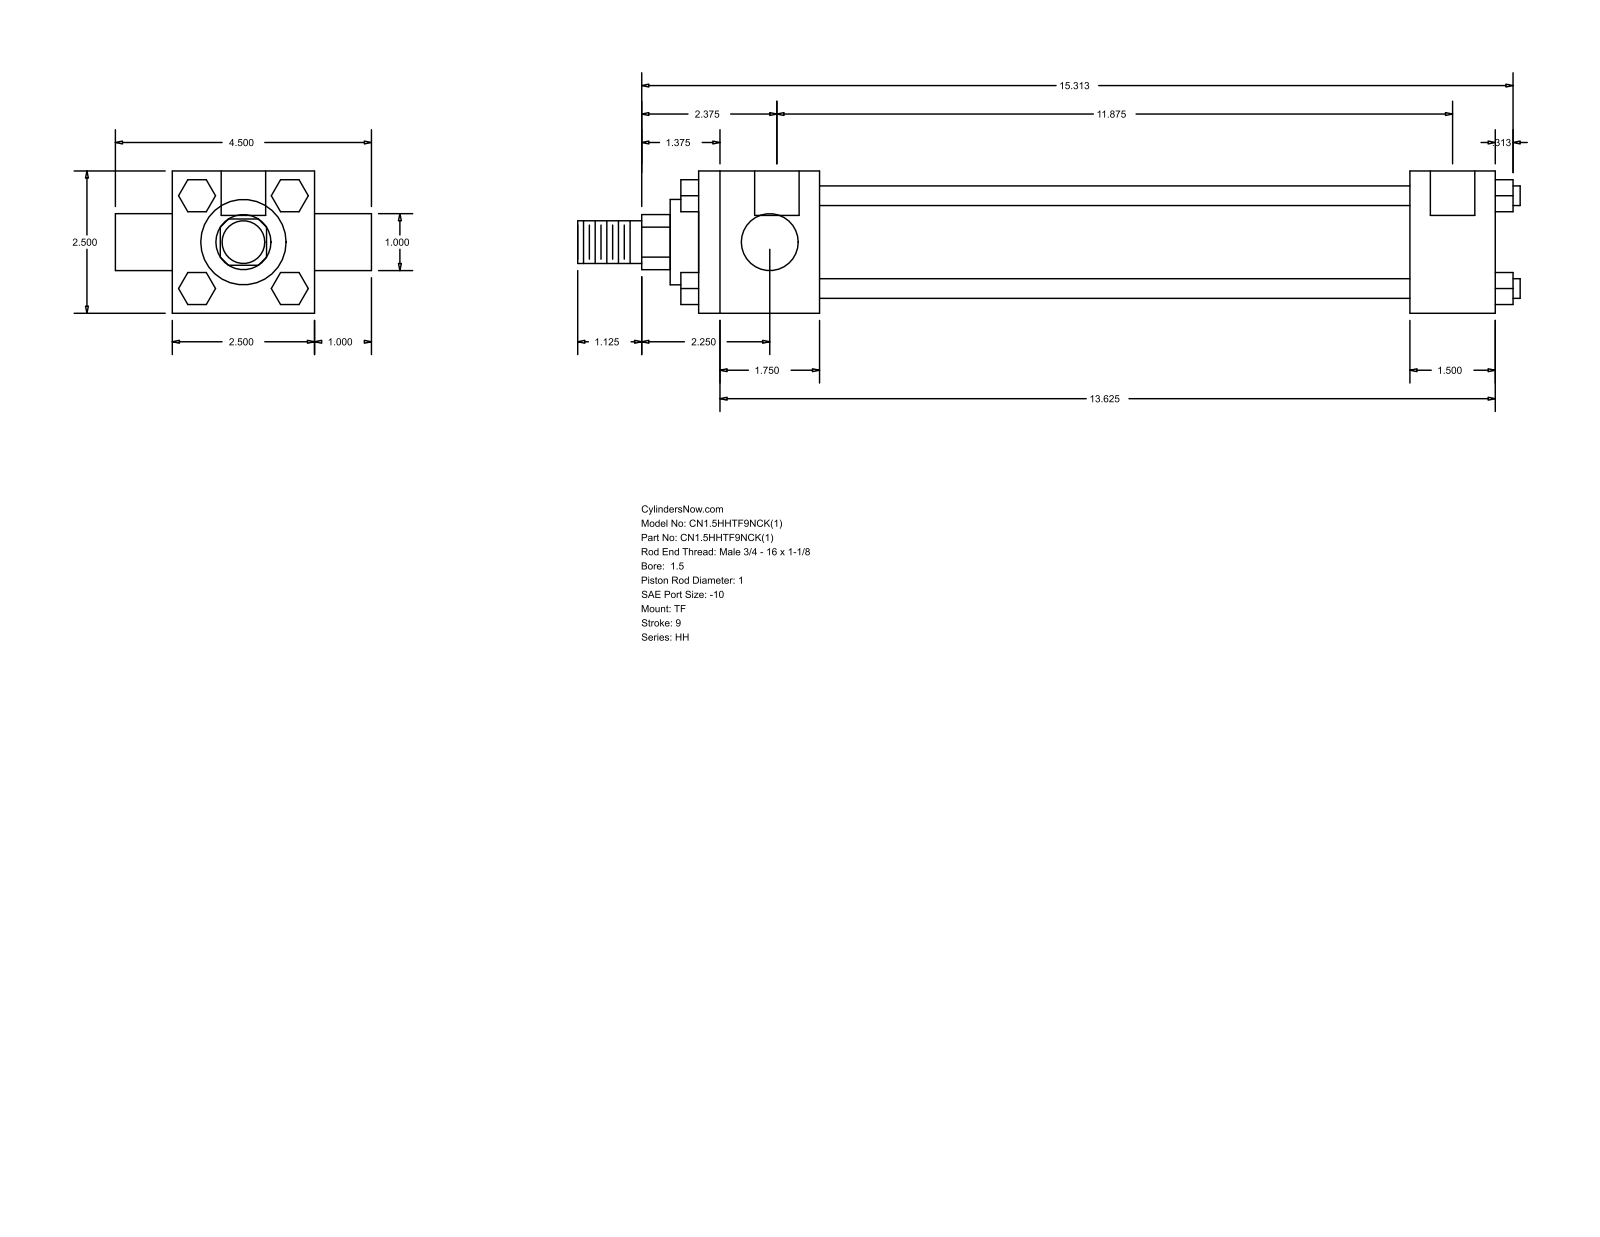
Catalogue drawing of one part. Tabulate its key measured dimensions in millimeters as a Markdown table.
| quantity | value |
| --- | --- |
| part name | HH_TF__0150_1 |
| STEP written by | GSSL Pune (CONFIG_CONTROL_DESIGN) |
| units | millimeters |
| bodies | 0 solids, 120 faces (92 planar, 28 cylindrical, 0 other) |
| overall size | 420.69 × 114.3 × 63.5 |
| round holes (diameter × count) | 5.56 × 3, 19.84 × 2 |
| round bosses / shafts (diameter × count) | 8.76 × 4, 25.4 × 2, 44.45 × 1, 38.1 × 1, 19.05 × 1 |
| partial cylindrical surfaces (radius × count) | 12.29 × 1 |
| main face-to-face distances | 63.5, 38.1, 301.62, 263.52, 53.98, 317.5, 355.6, 25.4, 20.7, 14.29 |
| hole center spacings | 1.59, 303.21, 301.62, 304.8 |
